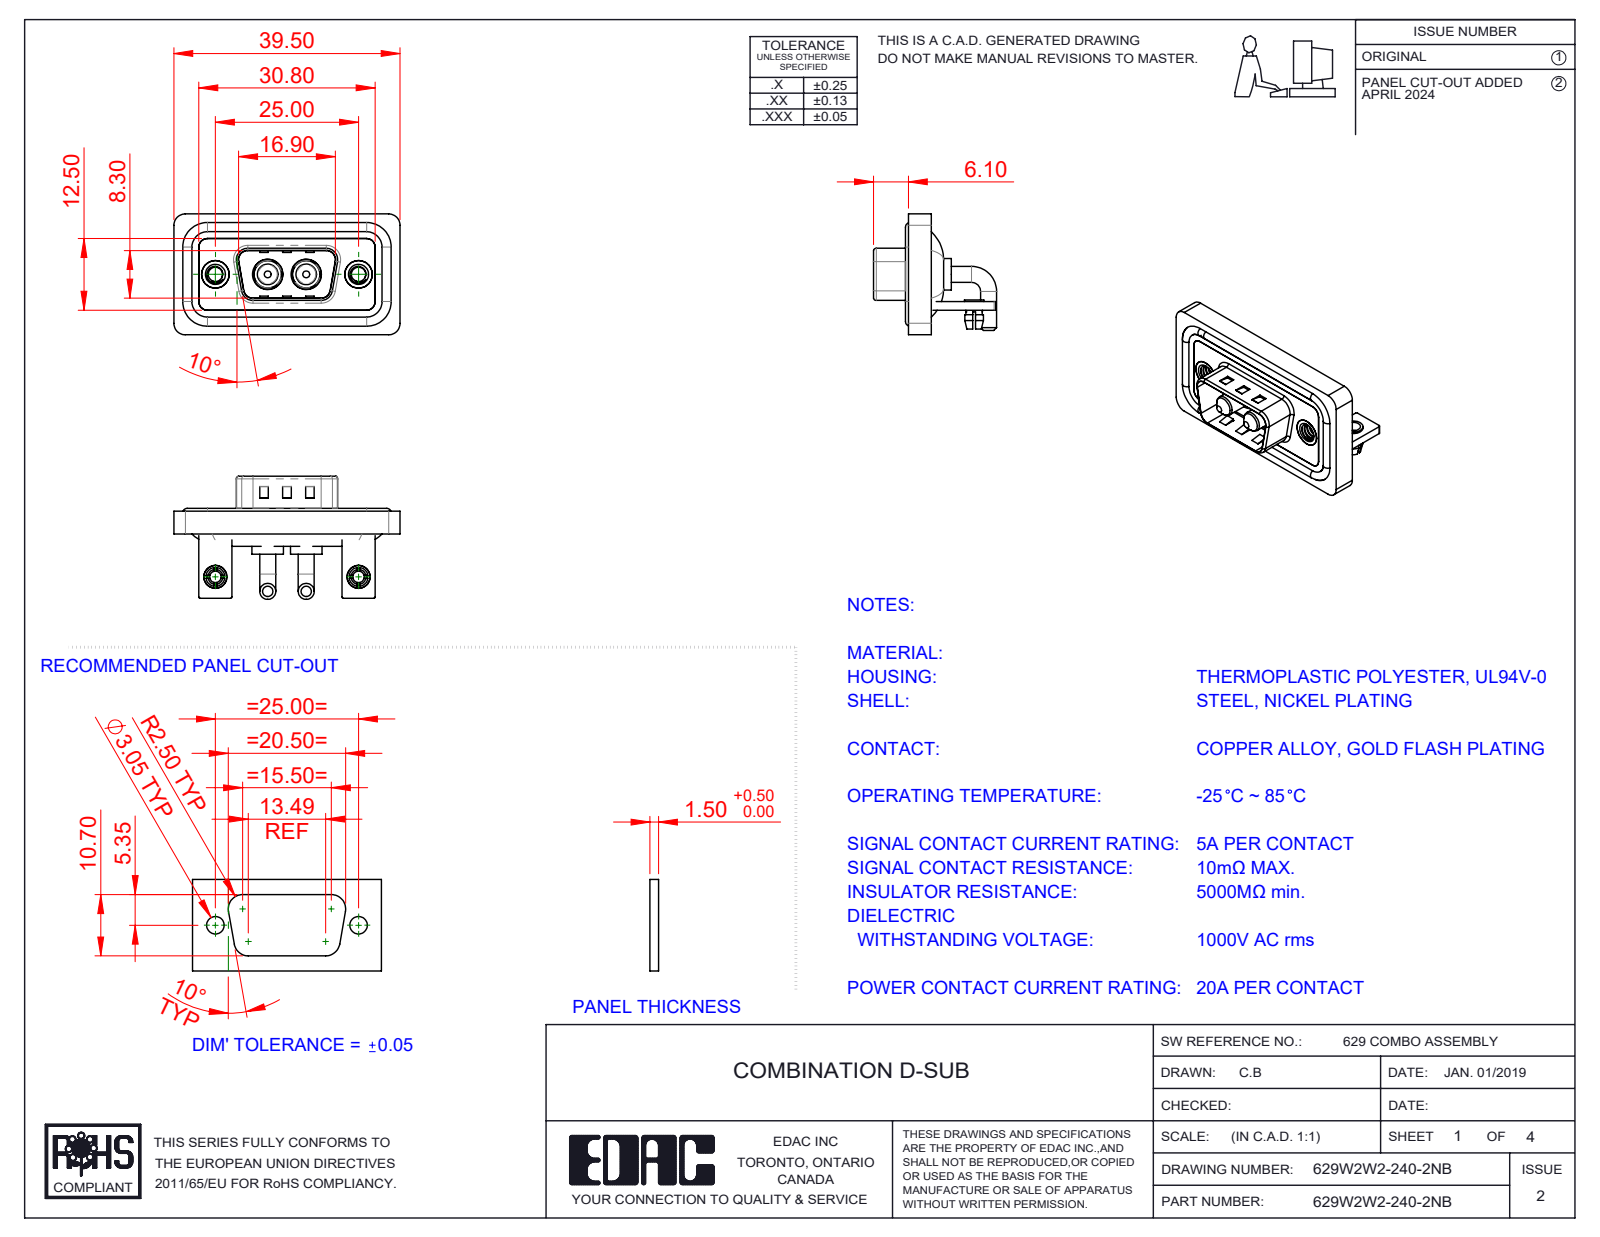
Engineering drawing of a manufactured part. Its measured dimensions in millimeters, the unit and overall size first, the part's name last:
Units: millimetres
Overall size (bounding box): 39.5 × 21.5 × 21.1
Round holes (diameter × count): ⌀2.5 ×4, ⌀2 ×2, ⌀3.2 ×2, ⌀4 ×2, ⌀4.8 ×2, ⌀4.85 ×2, ⌀5 ×2, ⌀5.3 ×2
Round bosses / shafts (diameter × count): ⌀2.8 ×4, ⌀1.6 ×4, ⌀5.5 ×2, ⌀5.2 ×2, ⌀4.9 ×2, ⌀4.75 ×2, ⌀4 ×2, ⌀3.75 ×2
Partial cylindrical surfaces — rounded edges, fillets, slot ends (radius × count): R2 ×19, R1.5 ×18, R0.25 ×16, R0.5 ×9, R1.6 ×8, R0.6 ×4, R0.65 ×4, R0.9 ×4
Main face-to-face distances: 0.4, 1.5, 2.9, 0.8, 1.1, 1.2, 2.1, 1.6, 3.7, 2.5
Hole centre spacings: 9.14, 15.86, 25, 6.72
Volume: 4 892 mm³ · Surface area: 7 966 mm²
Bodies: 15 solids, 627 faces (233 planar, 272 cylindrical, 122 other)
Part name (STEP PRODUCT): Power Pin_20A RA; 629Combo Board Lock; 629W2W2-140-2NB; 629Combo Shell Front_09 Contacts (+5 more)
STEP written by: SolidWorks 2023 (CONFIG_CONTROL_DESIGN)
